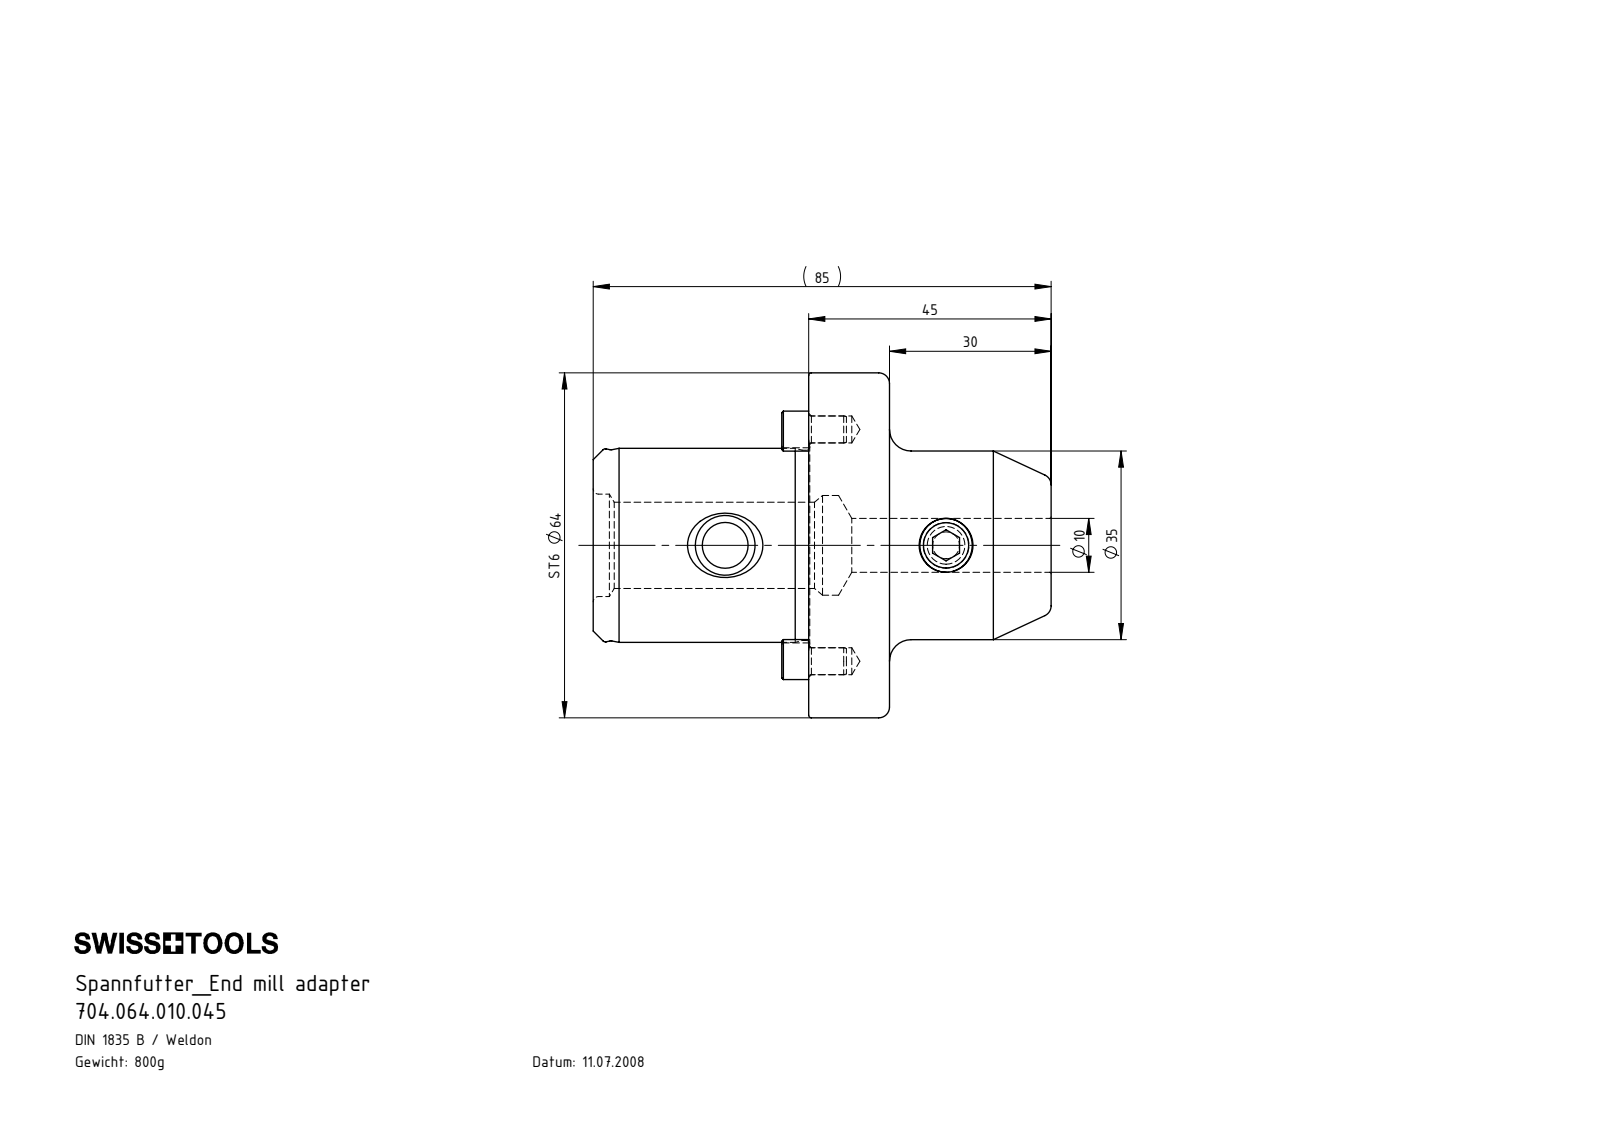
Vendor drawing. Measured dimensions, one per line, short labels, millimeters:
name: ST6-W10.K01.045; ST6-W10.K01.045_A; ST6-ER2.001.012_A; W10-ER1.001.012
written by: SolidWorks 2015 (CONFIG_CONTROL_DESIGN)
unit: mm
bodies: 4 solids, 147 faces (19 planar, 44 cylindrical, 84 other)
size: 85 × 64 × 64
volume: 101 868 mm³; area: 21 591 mm²
holes: 2× ⌀5, 2× ⌀8.5, 1× ⌀10, 1× ⌀16, 1× ⌀18.5, 1× ⌀19
bosses: 1× ⌀64, 1× ⌀36, 1× ⌀35.8, 1× ⌀35.3, 1× ⌀35, 1× ⌀10
rounds: 4× R0.5, 2× R5.47, 2× R18.05
face distances: 15, 40, 55, 85, 45, 30, 5, 35, 20, 50
hole spacings: 21.5, 41, 43
